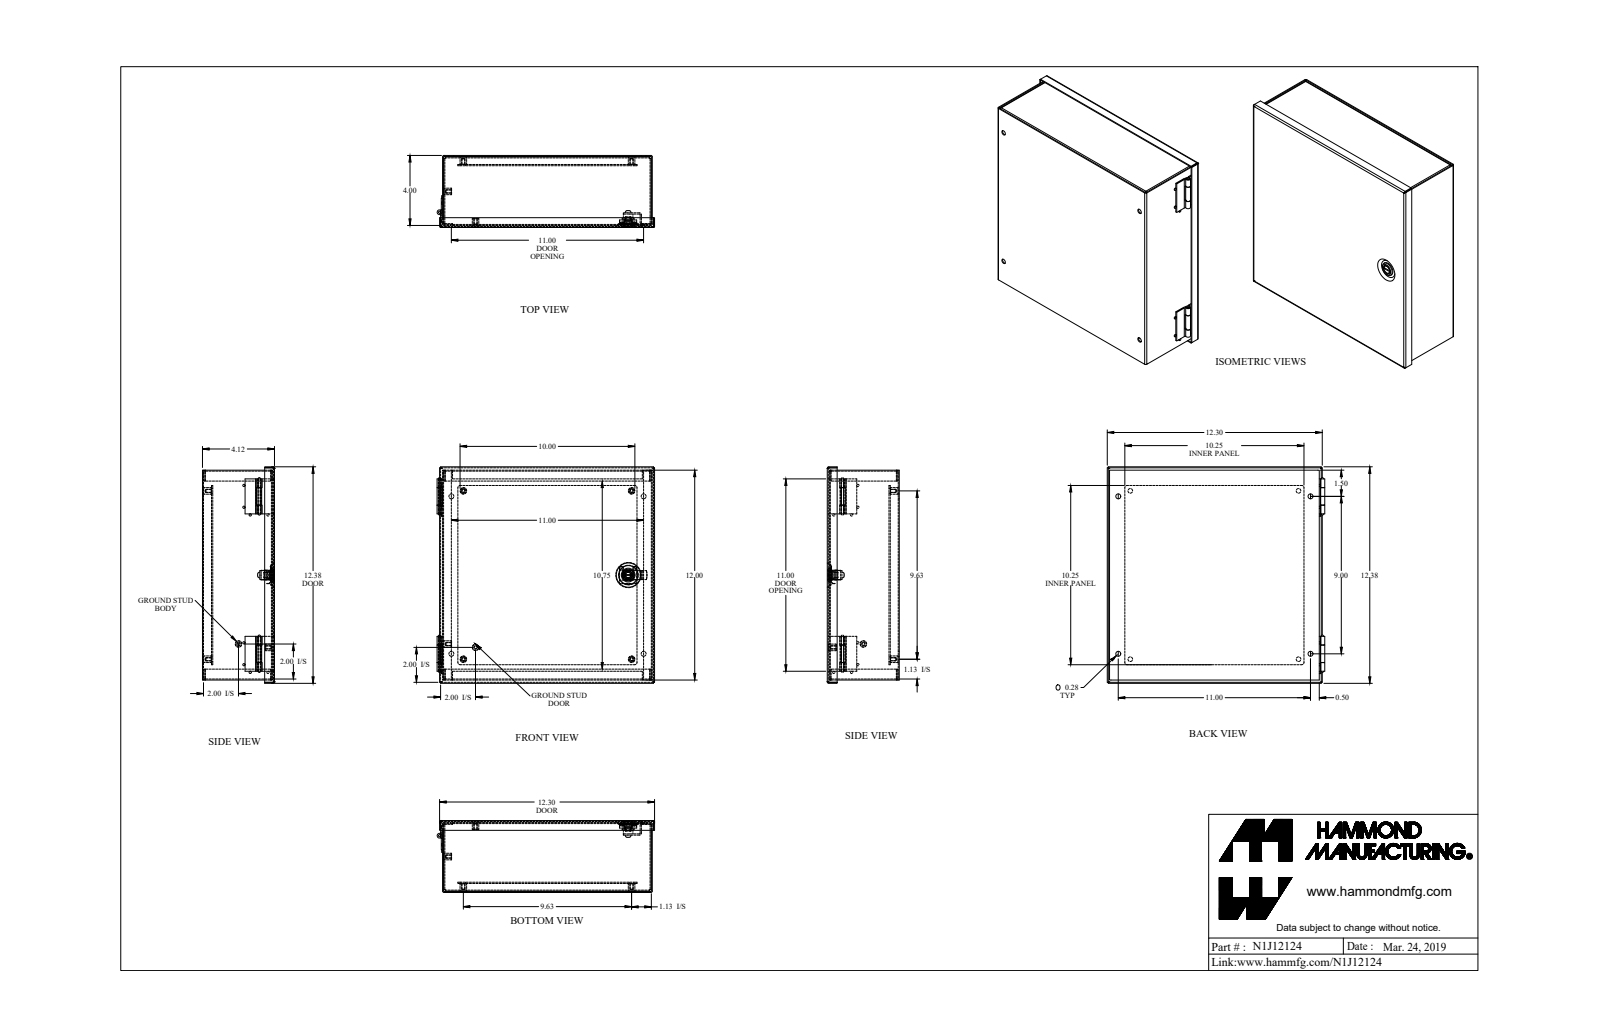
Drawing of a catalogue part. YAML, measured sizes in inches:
part_name: "N1J12124"
step_written_by: "SolidWorks 2018 (AUTOMOTIVE_DESIGN)"
units: inches
bodies: {solids: 18, faces: 477, planar: 224, cylindrical: 188, other: 65}
overall_size: [12.443, 12.38, 4.118]
volume: 39.89
surface_area: 1349
round_holes:
  - {diameter: 0.156, count: 6}
  - {diameter: 0.265, count: 4}
  - {diameter: 0.28, count: 4}
  - {diameter: 0.125, count: 1}
  - {diameter: 0.319, count: 1}
  - {diameter: 0.476, count: 1}
round_bosses_or_shafts:
  - {diameter: 0.131, count: 8}
  - {diameter: 0.375, count: 6}
  - {diameter: 0.787, count: 1}
  - {diameter: 0.547, count: 1}
  - {diameter: 0.472, count: 1}
  - {diameter: 0.469, count: 1}
  - {diameter: 0.366, count: 1}
  - {diameter: 0.32, count: 1}
partial_cylinders:
  - {radius: 0.029, count: 16}
  - {radius: 0.086, count: 16}
  - {radius: 0.012, count: 4}
  - {radius: 0.1, count: 4}
  - {radius: 0.125, count: 4}
  - {radius: 0.036, count: 2}
  - {radius: 0.079, count: 2}
  - {radius: 0.25, count: 2}
face_to_face_distances: [0.057, 4.061, 11.943, 4.004, 4.118, 0.072, 0.517, 0.46, 3.544, 3.601]
hole_center_spacings: [0.755, 9.338, 9.625, 10.317, 13.895, 4.586, 4.817, 9]
